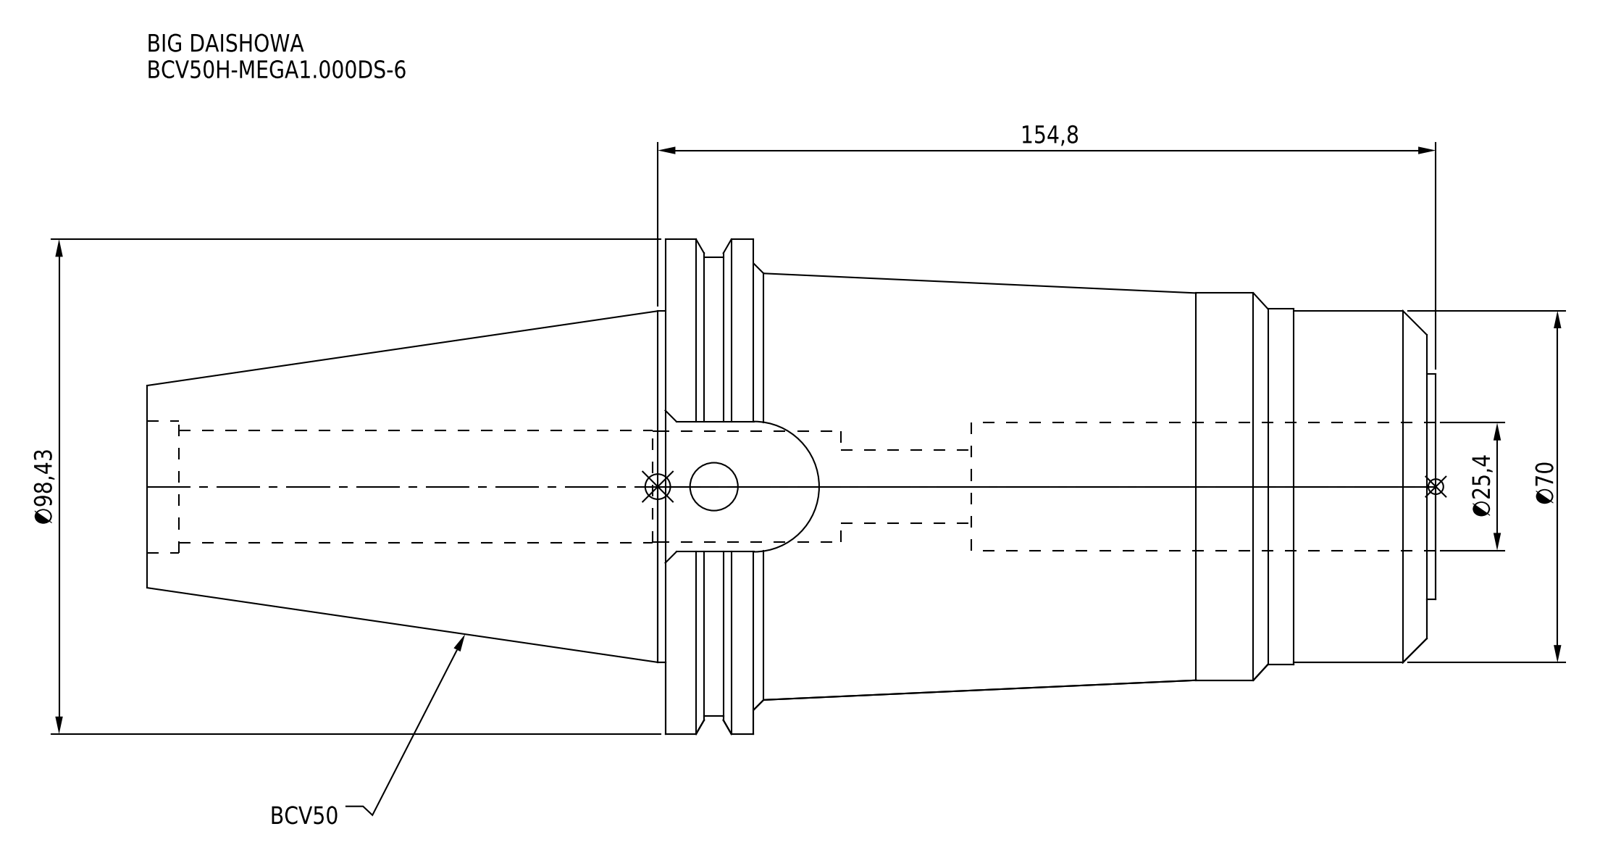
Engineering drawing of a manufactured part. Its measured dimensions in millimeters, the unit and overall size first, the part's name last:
Units: millimetres
Overall size (bounding box): 256.4 × 98.42 × 94.95
Round holes (diameter × count): ⌀9.53 ×1, ⌀14.5 ×1, ⌀22 ×1, ⌀22.3 ×1, ⌀25.4 ×1, ⌀26.23 ×1
Round bosses / shafts (diameter × count): ⌀98.42 ×1, ⌀91.29 ×1, ⌀77 ×1, ⌀70.7 ×1, ⌀70 ×1, ⌀69.85 ×1, ⌀44.8 ×1
Partial cylindrical surfaces — rounded edges, fillets, slot ends (radius × count): R12.96 ×1
Main face-to-face distances: 151.5, 133.95, 17.55, 1.8, 135.75, 153.3, 256.4, 254.6, 120.65, 103.1
Volume: 905 178 mm³ · Surface area: 85 962 mm²
Bodies: 1 solid, 72 faces (26 planar, 32 cylindrical, 14 other)
Part name (STEP PRODUCT): BCV50H-MEGA1_000DS-6
STEP written by: CREO PARAMETRIC BY PTC INC, 2016380 (AUTOMOTIVE_DESIGN)
